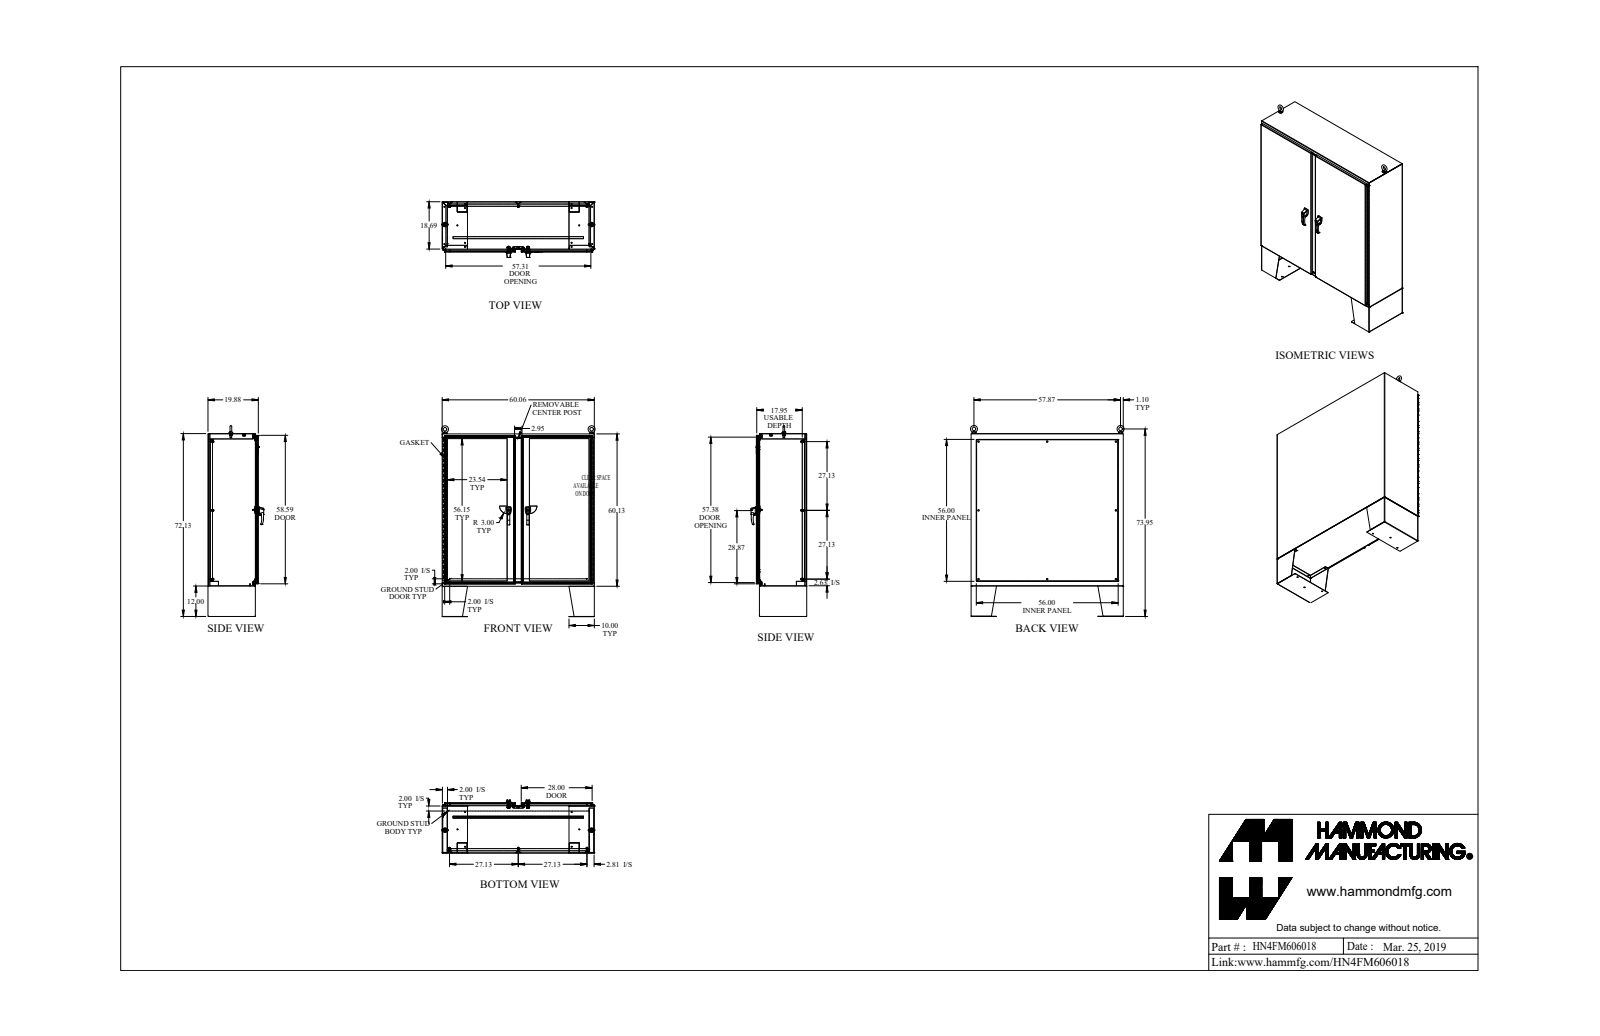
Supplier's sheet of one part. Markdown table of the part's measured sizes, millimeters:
| quantity | value |
| --- | --- |
| part name | HN4FM606018 |
| STEP written by | SolidWorks 2018 (AUTOMOTIVE_DESIGN) |
| units | millimeters |
| bodies | 130 solids, 3768 faces (1736 planar, 1659 cylindrical, 373 other) |
| overall size | 1913 × 1539.4 × 558.5 |
| volume | 31 660 000 mm³ |
| surface area | 25 020 000 mm² |
| round holes (diameter × count) | 7.7 × 20, 11.1 × 14, 7.8 × 8, 8.9 × 8, 14.3 × 8, 6.4 × 6, 11.3 × 6, 7.1 × 4, 8 × 4, 9.9 × 4, 5.1 × 3, 8 × 3 |
| round bosses / shafts (diameter × count) | 25.4 × 10, 16.5 × 8, 9.5 × 8, 8.4 × 8, 7.1 × 8, 19.1 × 4, 15.9 × 4, 11.2 × 4 |
| partial cylindrical surfaces (radius × count) | 12.7 × 33, 0.5 × 32, 3.2 × 32, 1.5 × 28, 1.2 × 27, 3.6 × 27, 0.8 × 12, 2.3 × 12 |
| main face-to-face distances | 2.4, 502.4, 500, 3.2, 457.1, 504.8, 45.3, 42.8, 459.6, 42.1 |
| hole center spacings | 152.4, 304.8, 457.2, 609.6, 1378, 762, 1486.2, 40.9 |
